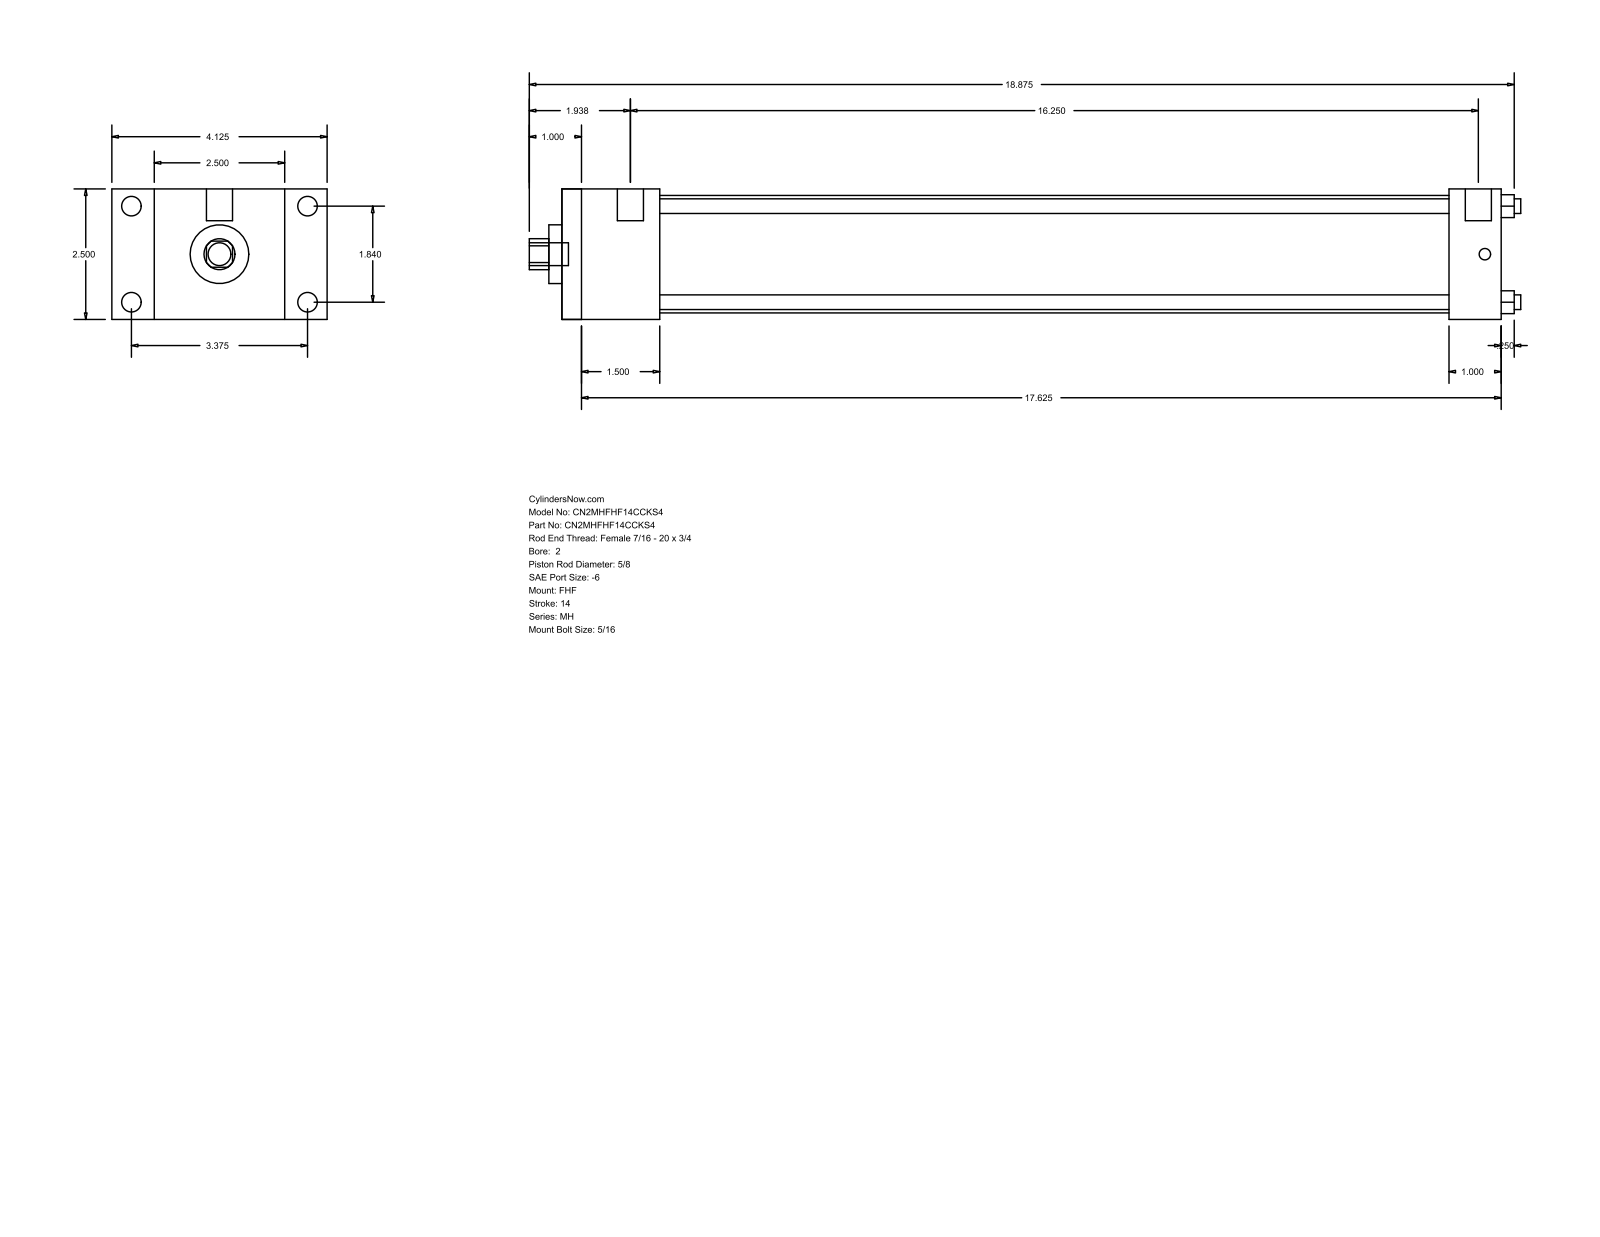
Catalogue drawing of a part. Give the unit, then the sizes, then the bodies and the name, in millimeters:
Units: millimetres
Overall size (bounding box): 482.6 × 104.78 × 63.5
Round holes (diameter × count): ⌀7.14 ×4, ⌀15.88 ×1, ⌀28.57 ×1, ⌀57.15 ×1
Round bosses / shafts (diameter × count): ⌀9.53 ×4, ⌀5.56 ×4, ⌀12.7 ×2, ⌀11.11 ×1
Partial cylindrical surfaces — rounded edges, fillets, slot ends (radius × count): R7.54 ×1
Main face-to-face distances: 63.5, 47.62, 457.19, 409.57, 20.64, 84.14, 104.78, 431.8, 384.18, 25.39
Hole centre spacings: 33.05, 46.74, 66.1
Bodies: 0 solids, 88 faces (60 planar, 28 cylindrical, 0 other)
Part name (STEP PRODUCT): MH_FHF__0200_0.625
STEP written by: GSSL Pune (CONFIG_CONTROL_DESIGN)
